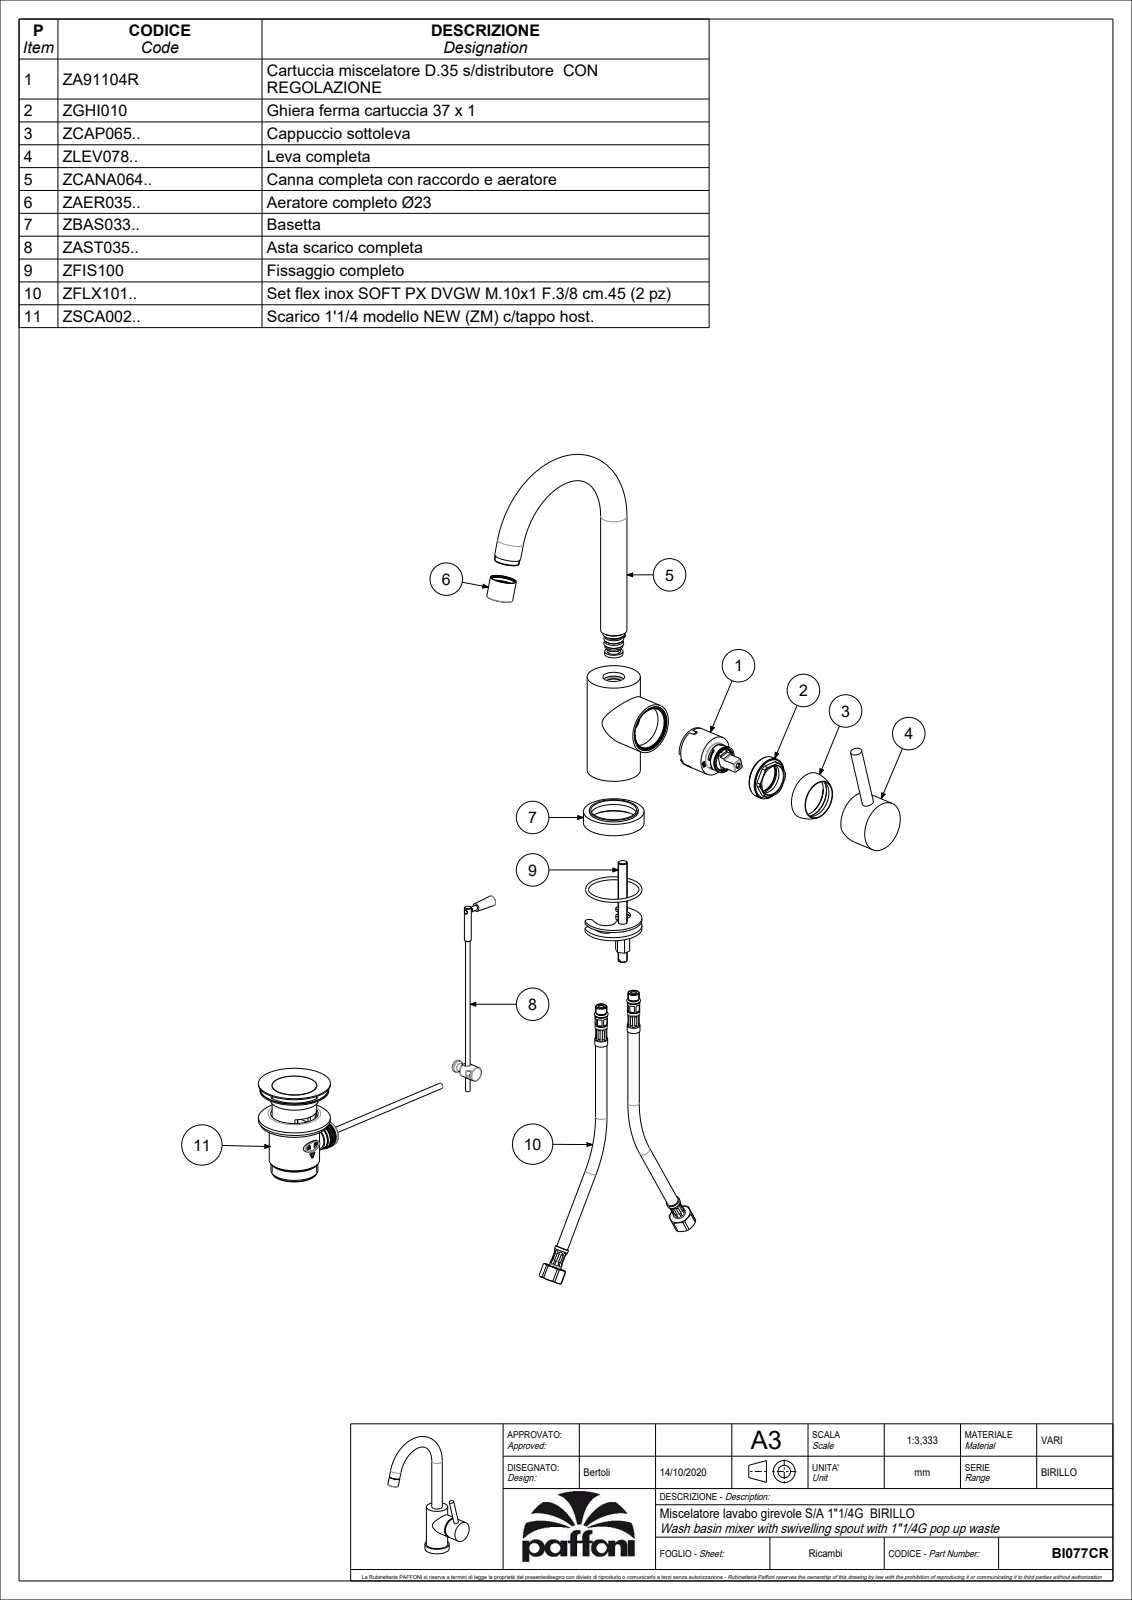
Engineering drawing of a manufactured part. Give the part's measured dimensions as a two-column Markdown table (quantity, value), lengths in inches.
| quantity | value |
| --- | --- |
| part name | BI077CR |
| STEP written by | CREO PARAMETRIC BY PTC INC, 2020044 (CONFIG_CONTROL_DESIGN) |
| units | inches |
| bodies | 7 solids, 1271 faces (686 planar, 370 cylindrical, 215 other) |
| overall size | 11.323 × 7.537 × 4.108 |
| volume | 13.25 in³ |
| surface area | 189.5 in² |
| round holes (diameter × count) | 0.256 × 5, 0.13 × 3, 0.354 × 3, 0.157 × 2, 0.177 × 2, 0.217 × 2, 0.394 × 2, 0.433 × 2, 0.709 × 2, 0.748 × 2, 1.575 × 2, 0.118 × 1 |
| round bosses / shafts (diameter × count) | 0.906 × 3, 0.441 × 2, 0.425 × 2, 0.394 × 2, 0.157 × 2, 2.087 × 1, 1.831 × 1, 1.732 × 1 |
| partial cylindrical surfaces (radius × count) | 0.02 × 27, 0.05 × 14, 0.081 × 14, 0.006 × 11, 0.012 × 4, 0.039 × 2, 0.089 × 2, 0.083 × 1 |
| main face-to-face distances | 0.354, 0.433, 2.953, 0.079, 0.591, 1.024, 3.976, 2.217, 0.039, 0.945 |
| hole center spacings | 0.432, 0.047, 0.197, 0.361, 0.365, 0.401, 0.419, 0.465 |
